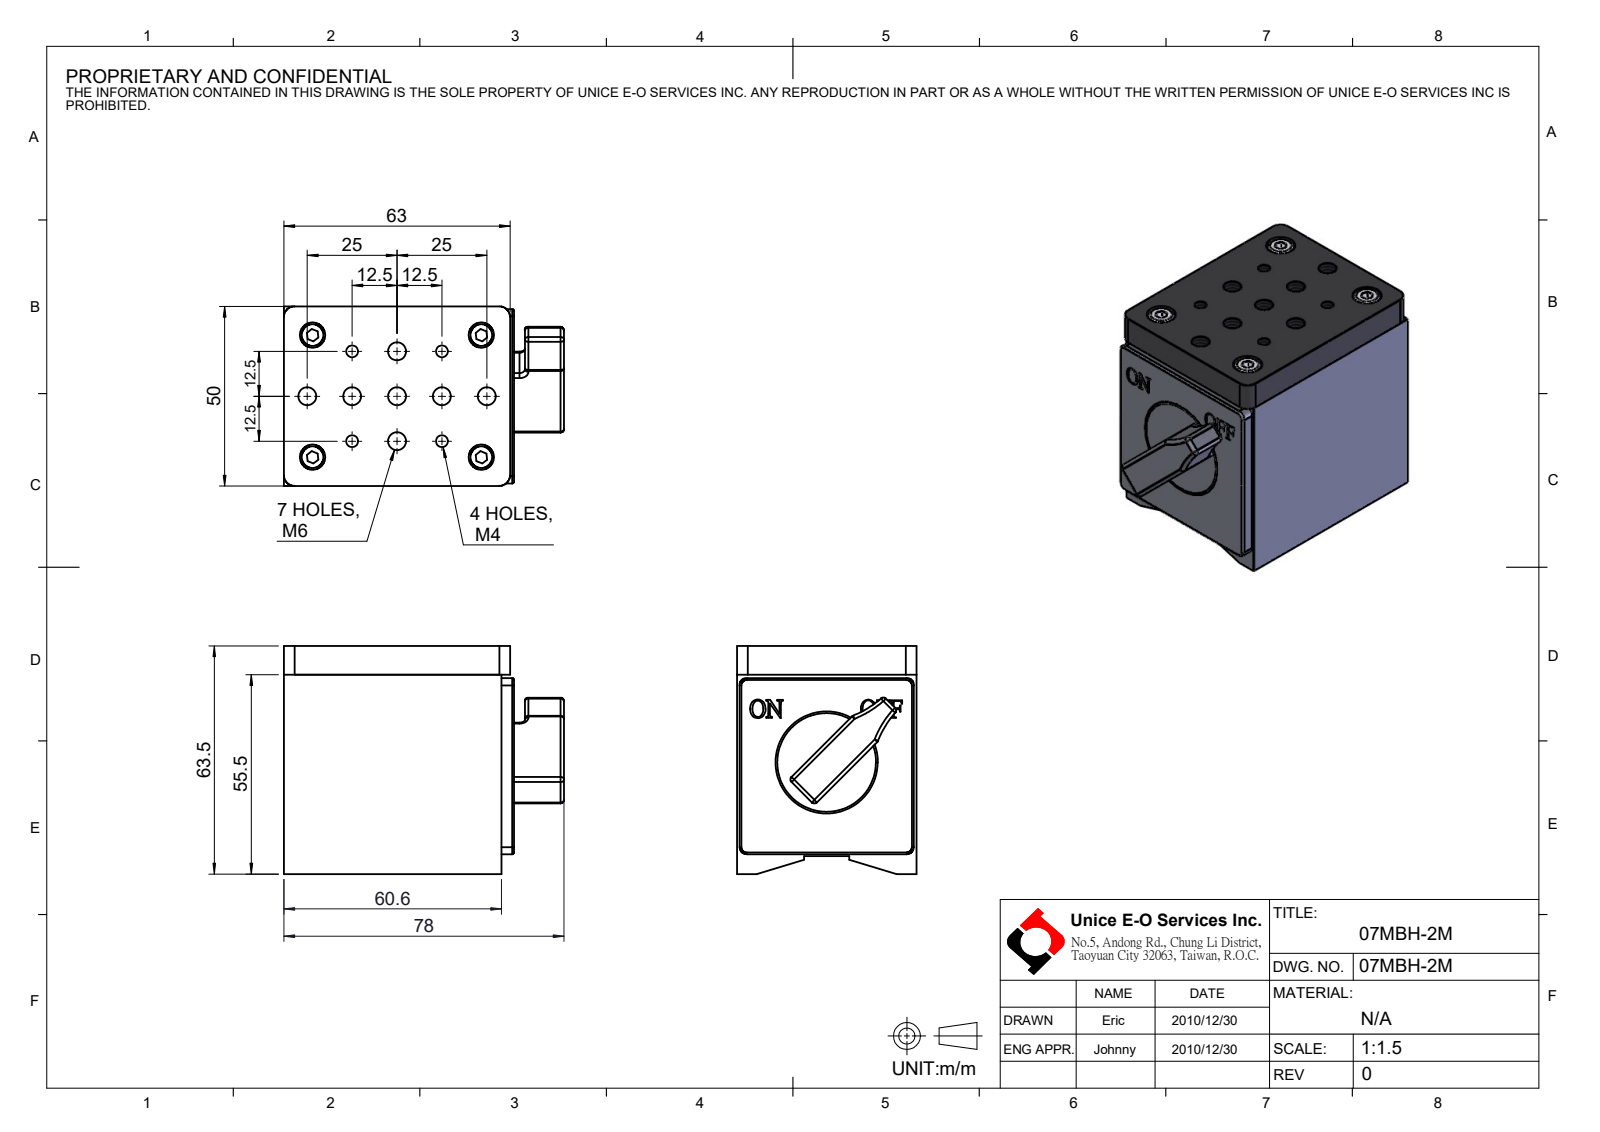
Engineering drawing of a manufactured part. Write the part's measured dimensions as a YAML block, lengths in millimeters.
part_name: "07MBH-2M"
step_written_by: "SolidWorks 2016 (CONFIG_CONTROL_DESIGN)"
units: millimeters
bodies: {solids: 6, faces: 348, planar: 134, cylindrical: 98, other: 116}
overall_size: [78, 63.5, 50]
volume: 194776
surface_area: 31188
round_holes:
  - {diameter: 3.3, count: 8}
  - {diameter: 5, count: 7}
  - {diameter: 4.5, count: 4}
  - {diameter: 8, count: 4}
  - {diameter: 28.5, count: 1}
round_bosses_or_shafts:
  - {diameter: 7, count: 4}
  - {diameter: 4, count: 4}
  - {diameter: 27.5, count: 1}
partial_cylinders:
  - {radius: 1, count: 15}
  - {radius: 0.5, count: 4}
  - {radius: 2, count: 4}
  - {radius: 3, count: 4}
  - {radius: 27.35, count: 2}
  - {radius: 1.5, count: 1}
face_to_face_distances: [50, 8, 63.1, 1, 5, 64.1, 58.5, 50.5, 63.5, 55.5]
hole_center_spacings: [12.5, 17.68, 27.95, 25, 11.88, 17.07, 20.25, 23.93]
